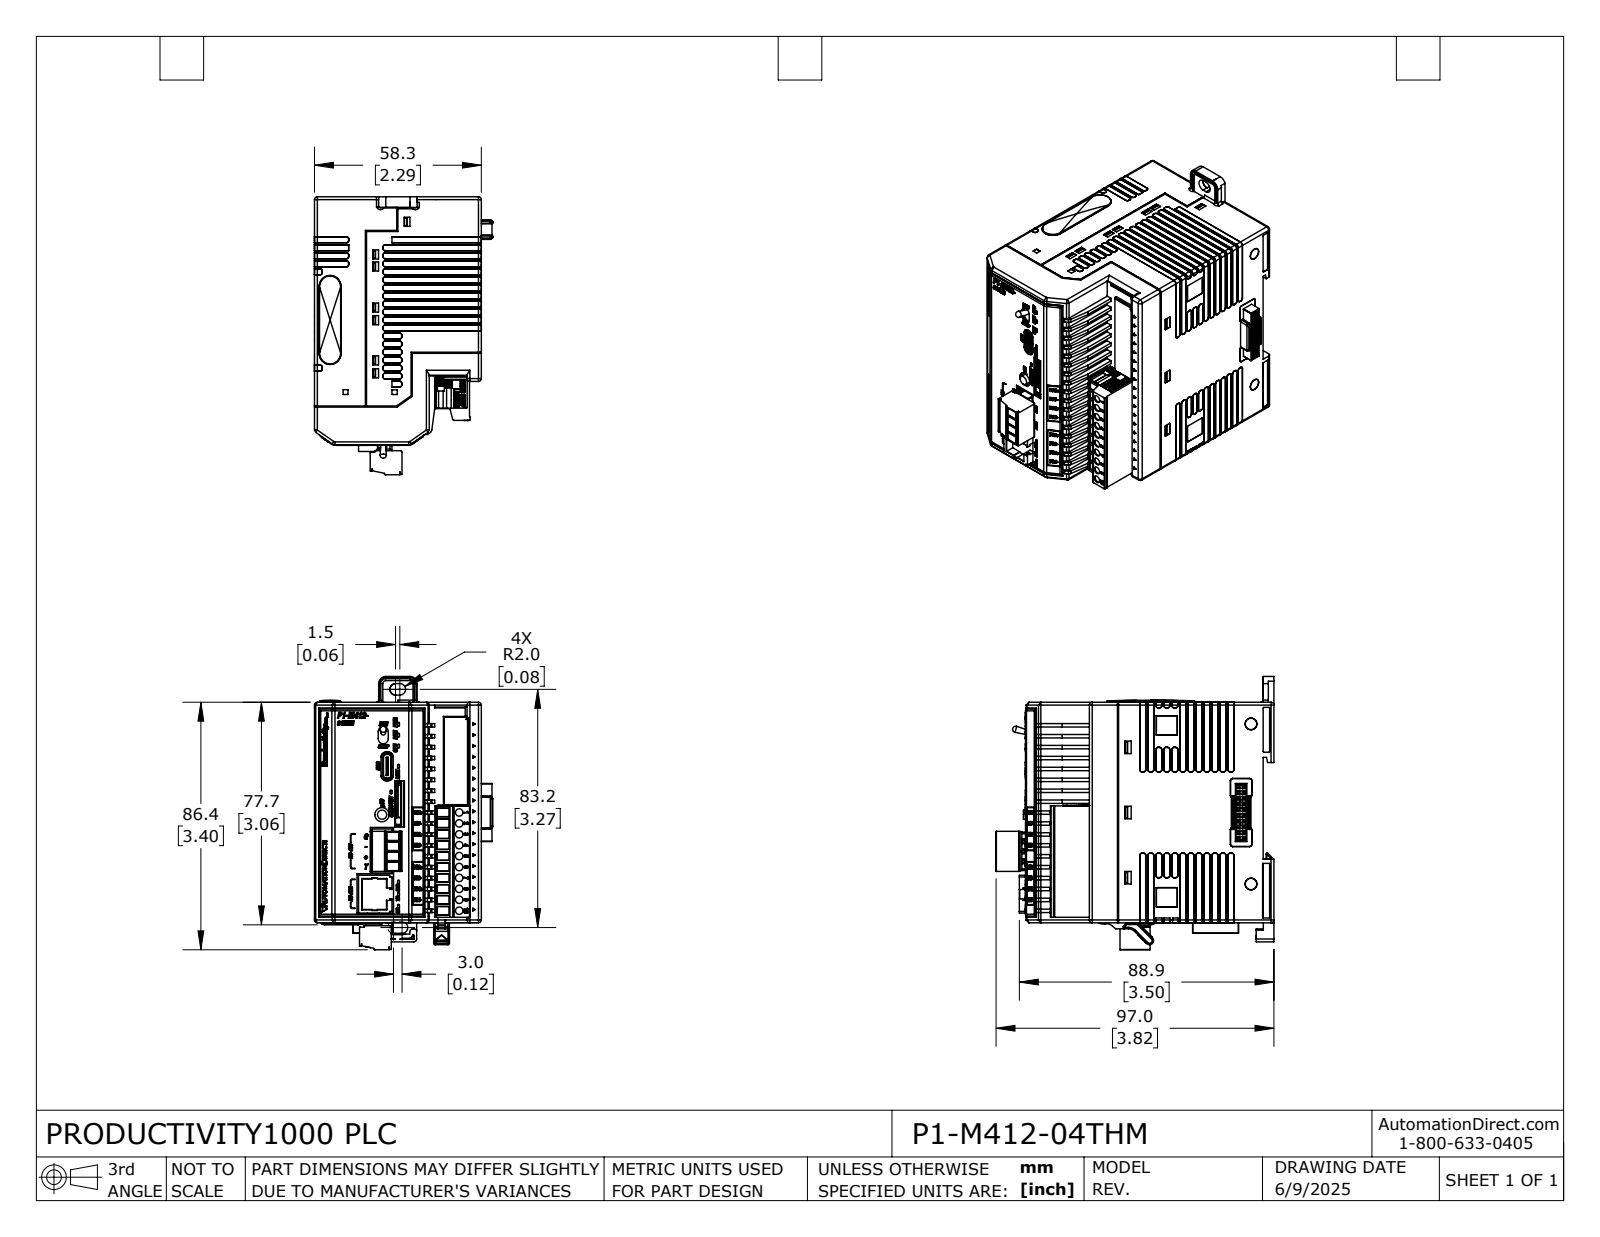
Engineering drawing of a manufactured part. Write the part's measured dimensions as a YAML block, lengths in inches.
part_name: "P1-M412-04THM"
step_written_by: "SolidWorks 2024 (AUTOMOTIVE_DESIGN)"
units: inches
bodies: {solids: 25, faces: 3708, planar: 2150, cylindrical: 901, other: 657}
overall_size: [3.686, 3.593, 2.452]
volume: 2.127
surface_area: 106.4
round_holes:
  - {diameter: 0.194, count: 1}
round_bosses_or_shafts:
  - {diameter: 0.214, count: 1}
  - {diameter: 0.126, count: 1}
partial_cylinders:
  - {radius: 0.01, count: 172}
  - {radius: 0.008, count: 86}
  - {radius: 0.02, count: 49}
  - {radius: 0.039, count: 33}
  - {radius: 0.079, count: 8}
  - {radius: 0.024, count: 7}
  - {radius: 0.004, count: 6}
  - {radius: 0.012, count: 4}
face_to_face_distances: [2.235, 0.02, 0.039, 2.275, 3.01, 3.022, 2.294, 2.294, 2.255, 3.02]
